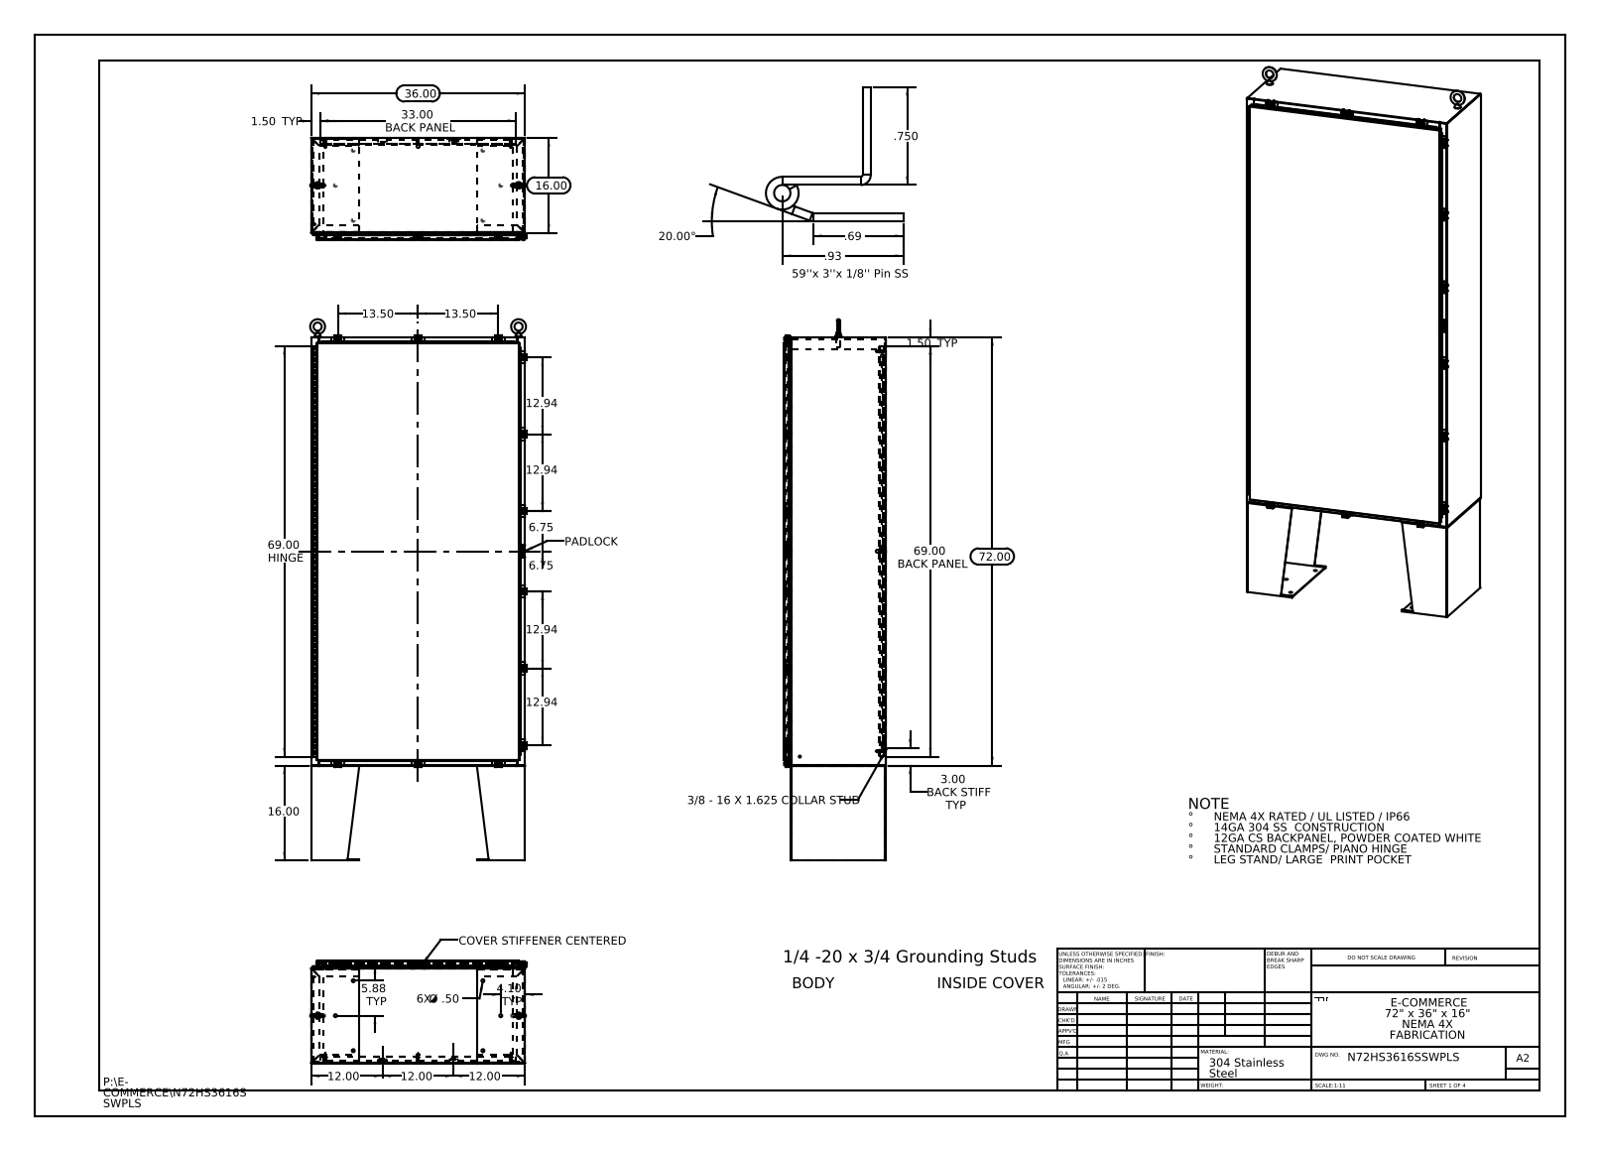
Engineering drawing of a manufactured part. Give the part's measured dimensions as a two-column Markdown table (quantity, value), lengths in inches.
| quantity | value |
| --- | --- |
| part name | N72HS3616SSWPLS Enclosure Stiffener; N72HS3616SSWPLS Bottom; Quarter-20 CD Stud; N72HS3616SSWPLS SD-LSK-Stand (+8 more) |
| STEP written by | SolidWorks 2013 (CONFIG_CONTROL_DESIGN) |
| units | inches |
| bodies | 98 solids, 4079 faces (2076 planar, 1711 cylindrical, 292 other) |
| overall size | 91 × 36.346 × 17.201 |
| volume | 1 156 in³ |
| surface area | 27 998 in² |
| round holes (diameter × count) | 0.5 × 14, 0.213 × 12, 0.26 × 12, 0.25 × 8, 0.75 × 4, 0.125 × 2, 0.125 × 1 |
| round bosses / shafts (diameter × count) | 0.25 × 13, 0.5 × 12, 0.399 × 12, 0.625 × 10, 0.375 × 8, 0.33 × 8, 0.157 × 8, 0.14 × 8 |
| partial cylindrical surfaces (radius × count) | 0.06 × 54, 0.013 × 39, 0.088 × 33, 0.12 × 24, 0.141 × 24, 0.05 × 19, 0.08 × 18, 0.09 × 18 |
| main face-to-face distances | 0.075, 17.126, 0.104, 17.051, 1.075, 17.201, 35.925, 16.126, 1, 16.051 |
| hole center spacings | 13.5, 2.225, 8.393, 13.663, 25.48, 28.397, 33.625, 35.789 |
